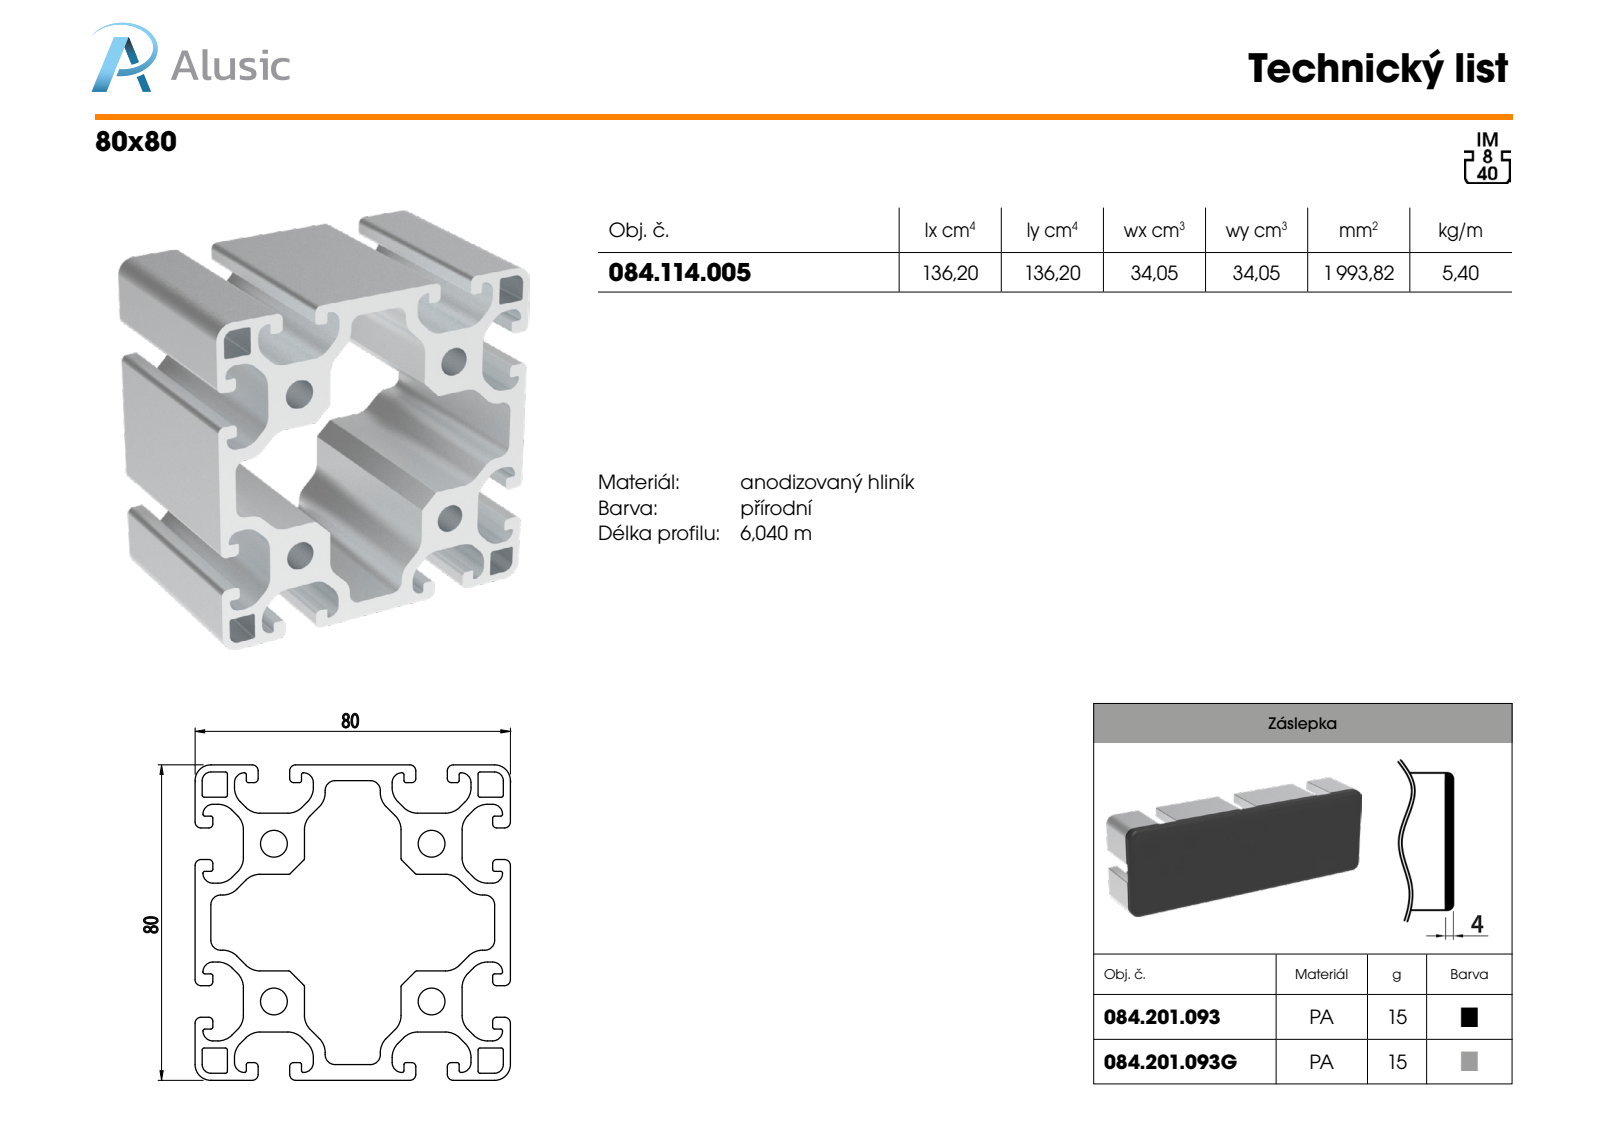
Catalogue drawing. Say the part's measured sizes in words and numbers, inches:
The part is named "084.114.005". Its 3-D file was written by "SolidWorks 2018 (AUTOMOTIVE_DESIGN)". It is 1 solid with 338 faces: 165 planar, 173 cylindrical and 0 other. Overall it measures 3.937 by 3.15 by 3.15 inches. Its volume is 12.17 cubic inches and its surface area 179.2 square inches. Round holes: 4 of diameter 0.268. Partial cylindrical surfaces (rounded edges, fillets, slot ends): 48 of radius 0.197, 36 of radius 0.02, 24 of radius 0.098, 16 of radius 0.018, 16 of radius 0.039, 16 of radius 0.059, 4 of radius 0.087, 4 of radius 0.157. The main face-to-face distances are 3.15, 1.575, 1.093, 2.057, 0.482, 2.667, 0.61, 0.323, 2.827, 0.159. The hole center spacings are 1.575, 2.227.
